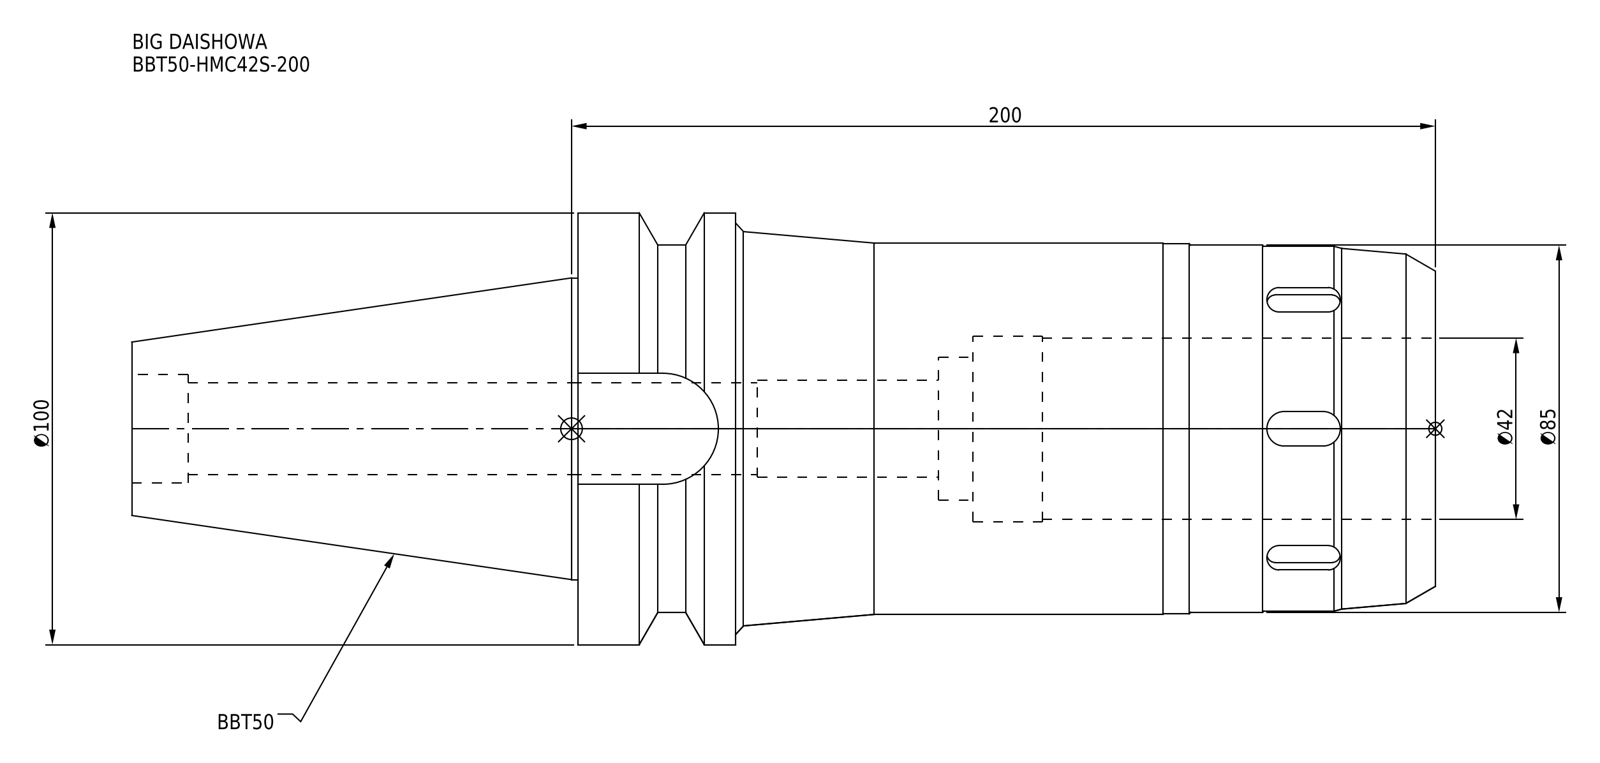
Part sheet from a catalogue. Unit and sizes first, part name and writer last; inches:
Units: inches
Overall size (bounding box): 11.882 × 3.937 × 3.937
Round holes (diameter × count): ⌀0.835 ×1, ⌀0.886 ×1, ⌀0.984 ×1, ⌀1.299 ×1, ⌀1.654 ×1, ⌀1.693 ×1
Round bosses / shafts (diameter × count): ⌀3.937 ×1, ⌀3.386 ×1, ⌀3.374 ×1, ⌀3.346 ×1, ⌀3.327 ×1, ⌀2.75 ×1
Partial cylindrical surfaces — rounded edges, fillets, slot ends (radius × count): R0.157 ×12, R0.506 ×1
Main face-to-face distances: 7.815, 11.882, 4.067, 2.787, 6.378, 1.437, 5.504, 0.315, 4.213, 2.165
Volume: 73.41 in³ · Surface area: 177.5 in²
Bodies: 1 solid, 106 faces (40 planar, 46 cylindrical, 20 other)
Part name (STEP PRODUCT): BBT50-HMC42S-200
STEP written by: CREO PARAMETRIC BY PTC INC, 2016380 (AUTOMOTIVE_DESIGN)
